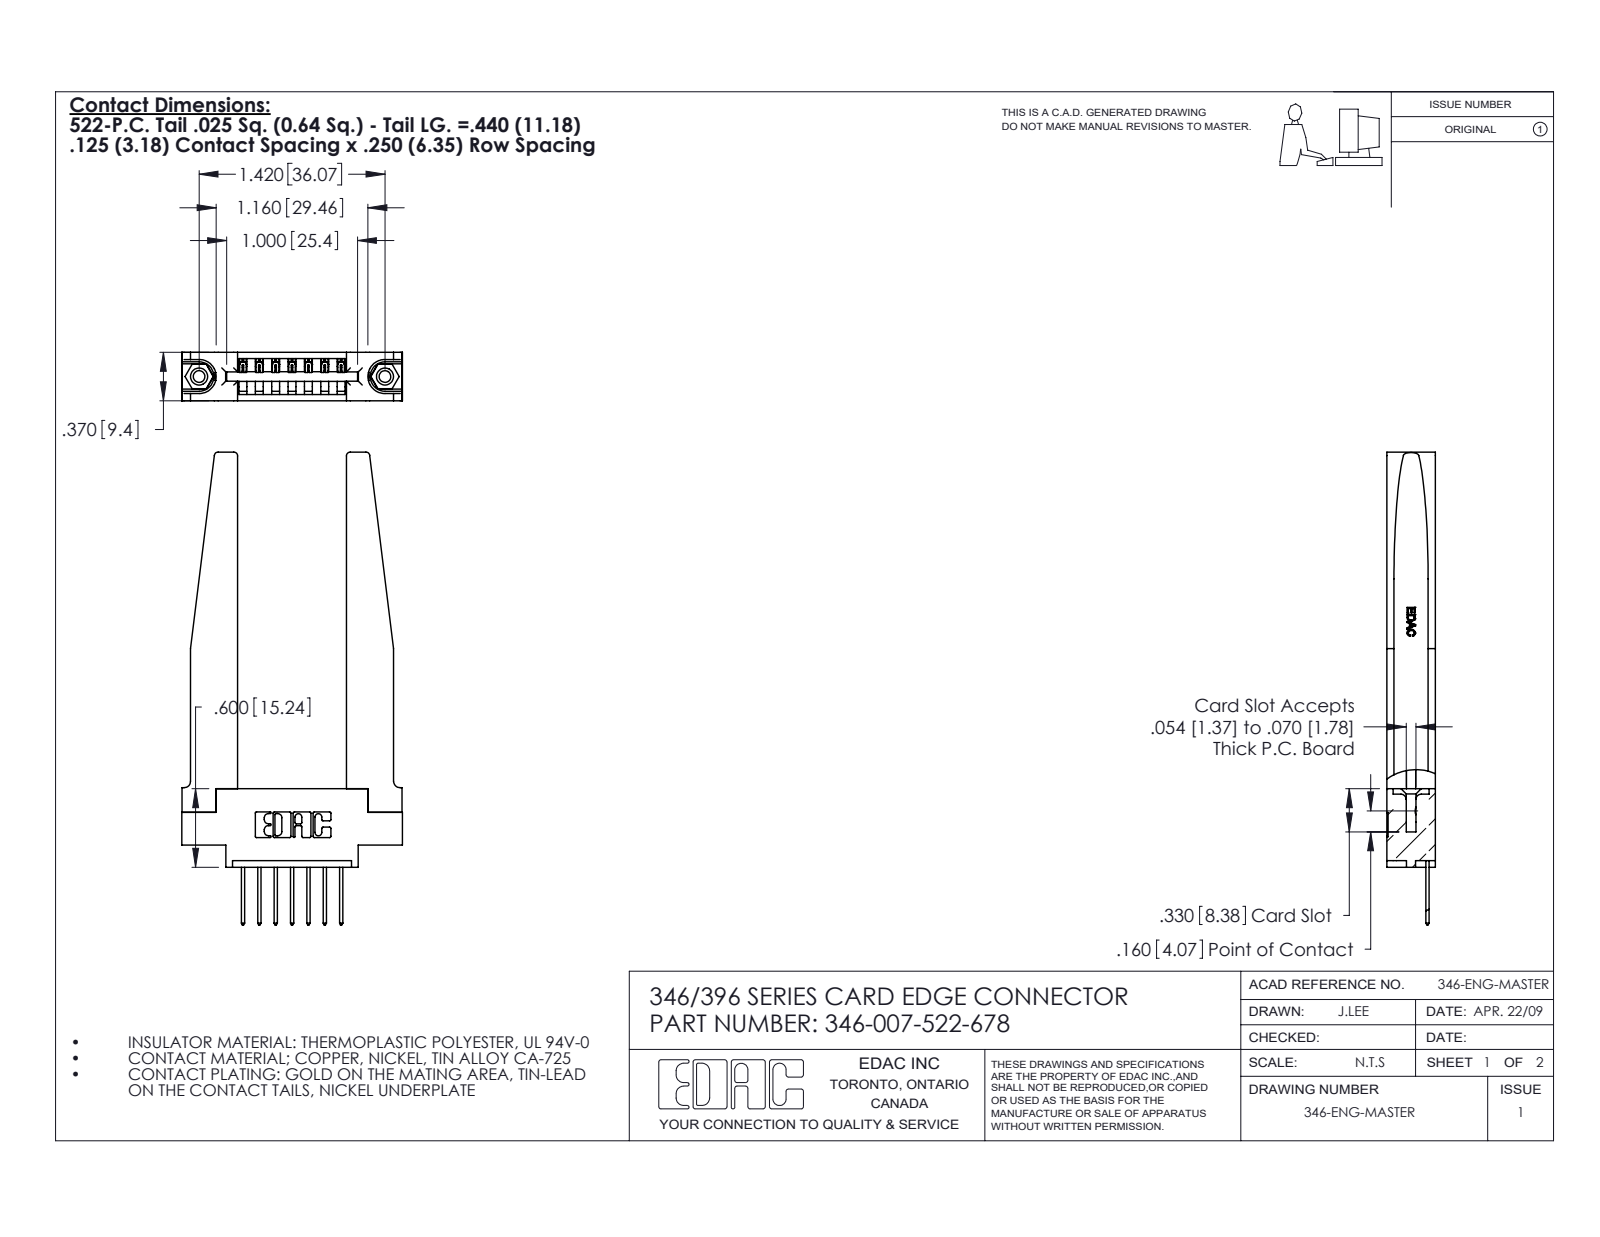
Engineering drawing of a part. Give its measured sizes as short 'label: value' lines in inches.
name: 346-007-522-678; 345-292-001_345-293-122; 345-250-001_345-250-001-102; 346-220-078_345-220-078 (+1 more)
written by: SolidWorks 2020 (CONFIG_CONTROL_DESIGN)
unit: in
bodies: 12 solids, 780 faces (516 planar, 212 cylindrical, 52 other)
size: 3.61 × 1.685 × 0.37
volume: 0.646 in³; area: 17.03 in²
holes: 2× ⌀0.089, 2× ⌀0.125, 2× ⌀0.156, 1× ⌀0.064
bosses: 2× ⌀0.155
rounds: 22× R0.01, 14× R0.006, 14× R0.01, 8× R0.03, 6× R0.007, 6× R0.031, 3× R0.026, 2× R0.031
face distances: 0.37, 0.15, 0.22, 0.072, 0.148, 0.25, 0.831, 0.048, 0.322, 0.102
hole spacings: 0.246, 1.217, 1.42
